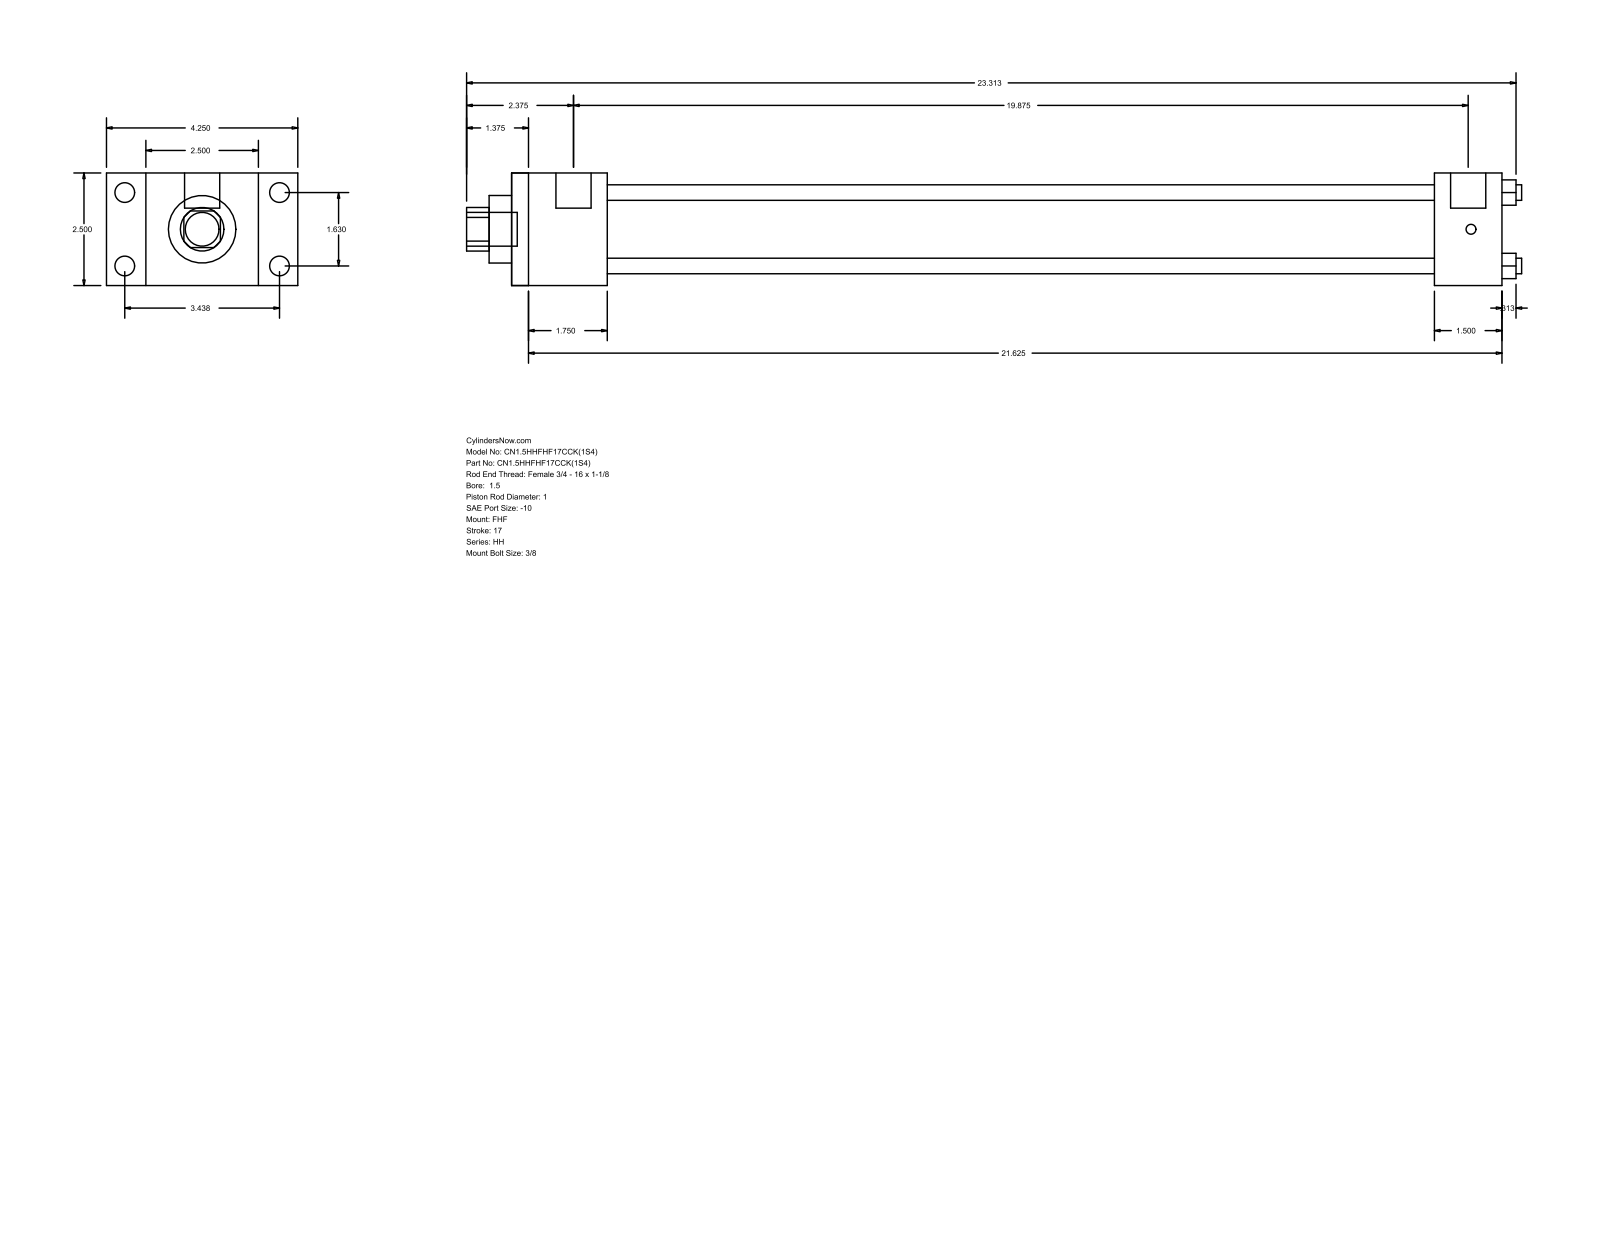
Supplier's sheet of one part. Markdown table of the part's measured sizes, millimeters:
| quantity | value |
| --- | --- |
| part name | HH_FHF__0150_1 |
| STEP written by | GSSL Pune (CONFIG_CONTROL_DESIGN) |
| units | millimeters |
| bodies | 0 solids, 88 faces (60 planar, 28 cylindrical, 0 other) |
| overall size | 595.31 × 107.95 × 63.5 |
| round holes (diameter × count) | 8.76 × 4, 25.4 × 1, 38.1 × 1, 44.45 × 1 |
| round bosses / shafts (diameter × count) | 11.13 × 4, 5.56 × 4, 19.84 × 2, 19.05 × 1 |
| partial cylindrical surfaces (radius × count) | 12.29 × 1 |
| main face-to-face distances | 63.5, 22.23, 85.73, 53.98, 107.96, 558.8, 504.82, 520.7, 466.72, 38.1 |
| hole center spacings | 29.27, 41.4, 58.55 |
